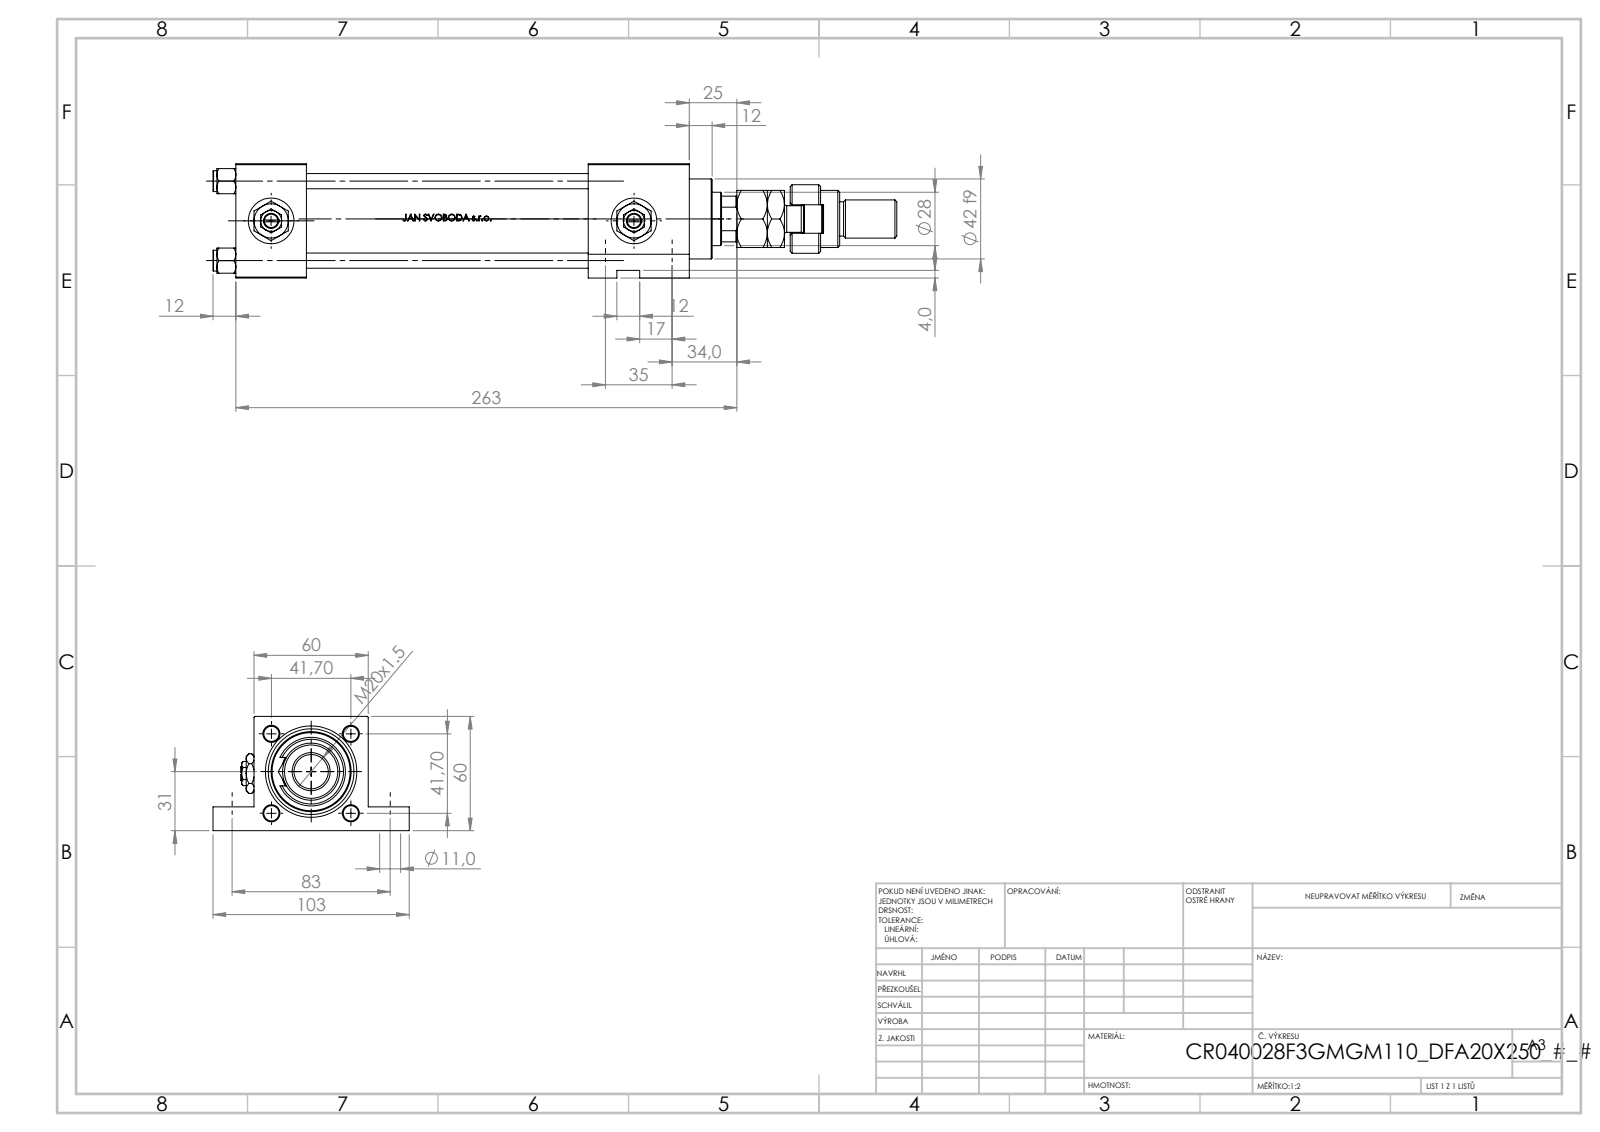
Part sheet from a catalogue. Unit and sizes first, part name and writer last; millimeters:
Units: millimetres
Overall size (bounding box): 359 × 103 × 60
Round holes (diameter × count): ⌀8 ×4, ⌀11 ×4, ⌀16.66 ×3, ⌀24 ×3, ⌀2.5 ×2, ⌀7 ×2, ⌀16 ×1, ⌀18.5 ×1, ⌀28 ×1, ⌀31 ×1, ⌀40 ×1, ⌀45 ×1
Round bosses / shafts (diameter × count): ⌀11 ×4, ⌀46 ×1, ⌀42 ×1, ⌀36 ×1, ⌀30 ×1, ⌀22 ×1, ⌀20 ×1, ⌀18 ×1
Partial cylindrical surfaces — rounded edges, fillets, slot ends (radius × count): R7.5 ×1, R12 ×1, R13.5 ×1
Main face-to-face distances: 60, 37, 53, 185, 148, 238, 38, 201, 15, 12.5
Hole centre spacings: 20.85, 29.49, 41.7, 46.53, 20.75, 35, 58.97, 83
Volume: 600 596 mm³ · Surface area: 175 206 mm²
Bodies: 15 solids, 1301 faces (514 planar, 161 cylindrical, 626 other)
Part name (STEP PRODUCT): Zatka_pro_OIL_PORT; FEMALE_PART_FOR_DFA; V215CR_VCP_F; NUT_M5_F (+4 more)
STEP written by: SolidWorks 2019 (CONFIG_CONTROL_DESIGN)
